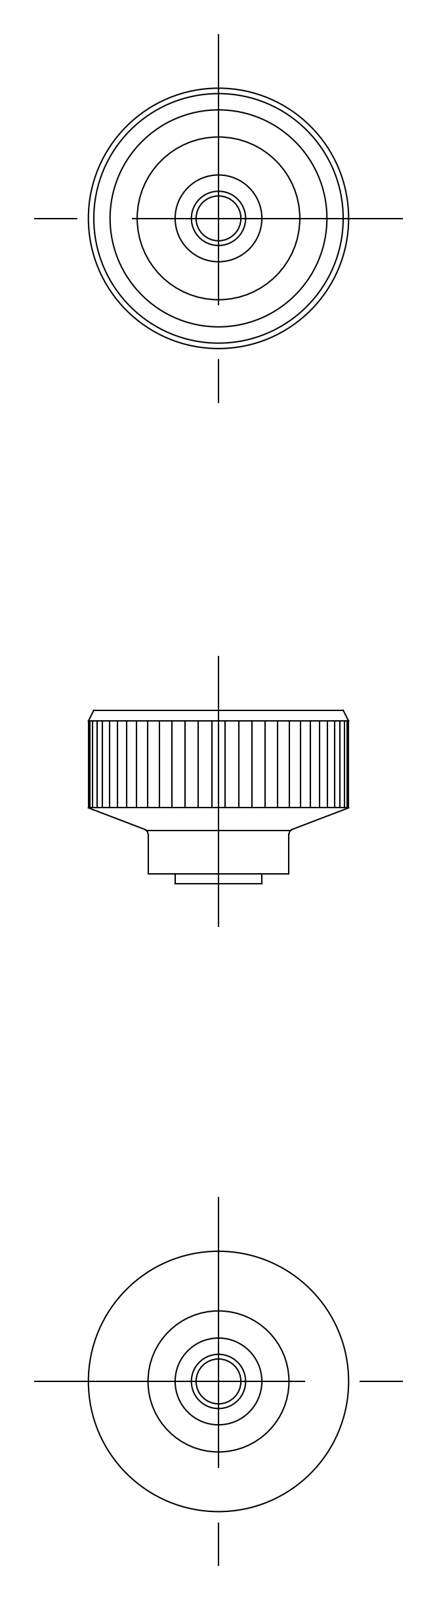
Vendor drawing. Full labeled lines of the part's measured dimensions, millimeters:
Part name (STEP PRODUCT): screw; knob; KKF_24_M5_4499_36
STEP written by: CADfix (AUTOMOTIVE_DESIGN)
Units: millimetres
Bodies: 2 solids, 31 faces (0 planar, 0 cylindrical, 31 other)
Overall size (bounding box): 24 × 24 × 16
Volume: 3 476 mm³ · Surface area: 2 507 mm²
